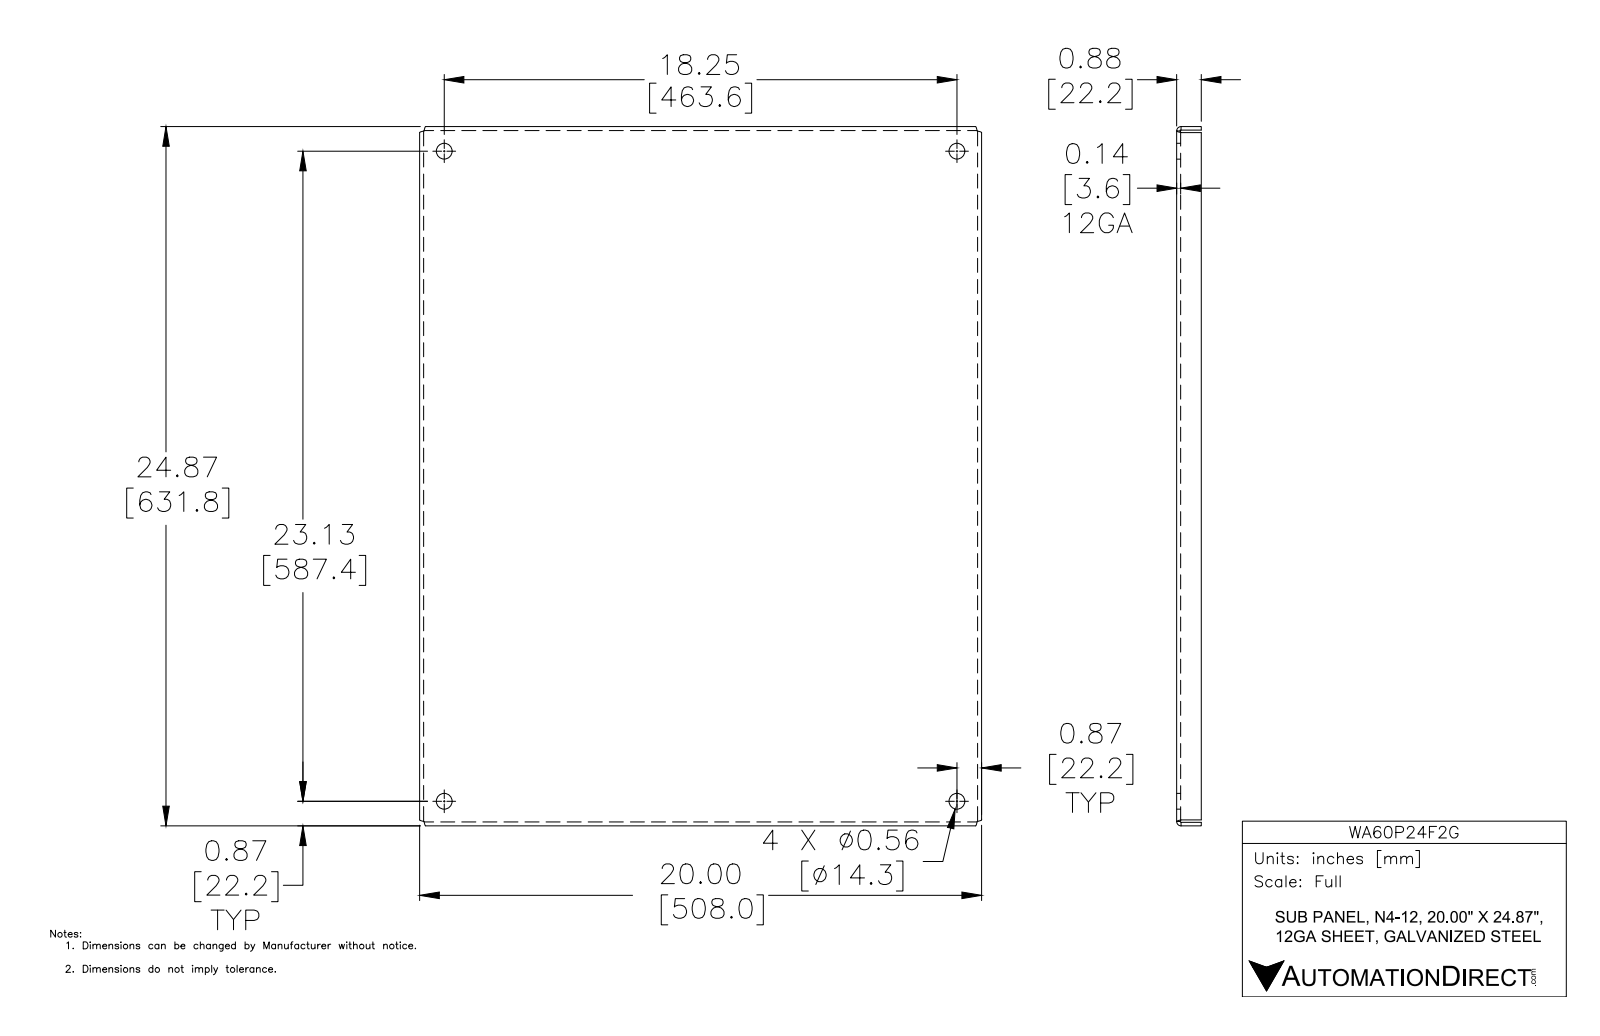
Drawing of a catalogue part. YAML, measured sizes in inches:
part_name: "WA_P_F_G"
step_written_by: "Autodesk Inventor 2012 (AUTOMOTIVE_DESIGN)"
units: inches
bodies: {solids: 1, faces: 42, planar: 22, cylindrical: 12, other: 8}
overall_size: [24.88, 20, 0.875]
volume: 52.81
surface_area: 1136
round_holes:
  - {diameter: 0.563, count: 4}
partial_cylinders:
  - {radius: 0.016, count: 4}
  - {radius: 0.109, count: 4}
face_to_face_distances: [0.094, 19.906, 24.786, 20, 19.813, 24.88, 24.693, 0.781, 0.875, 0.16]
hole_center_spacings: [18.25, 23.13, 29.463]
